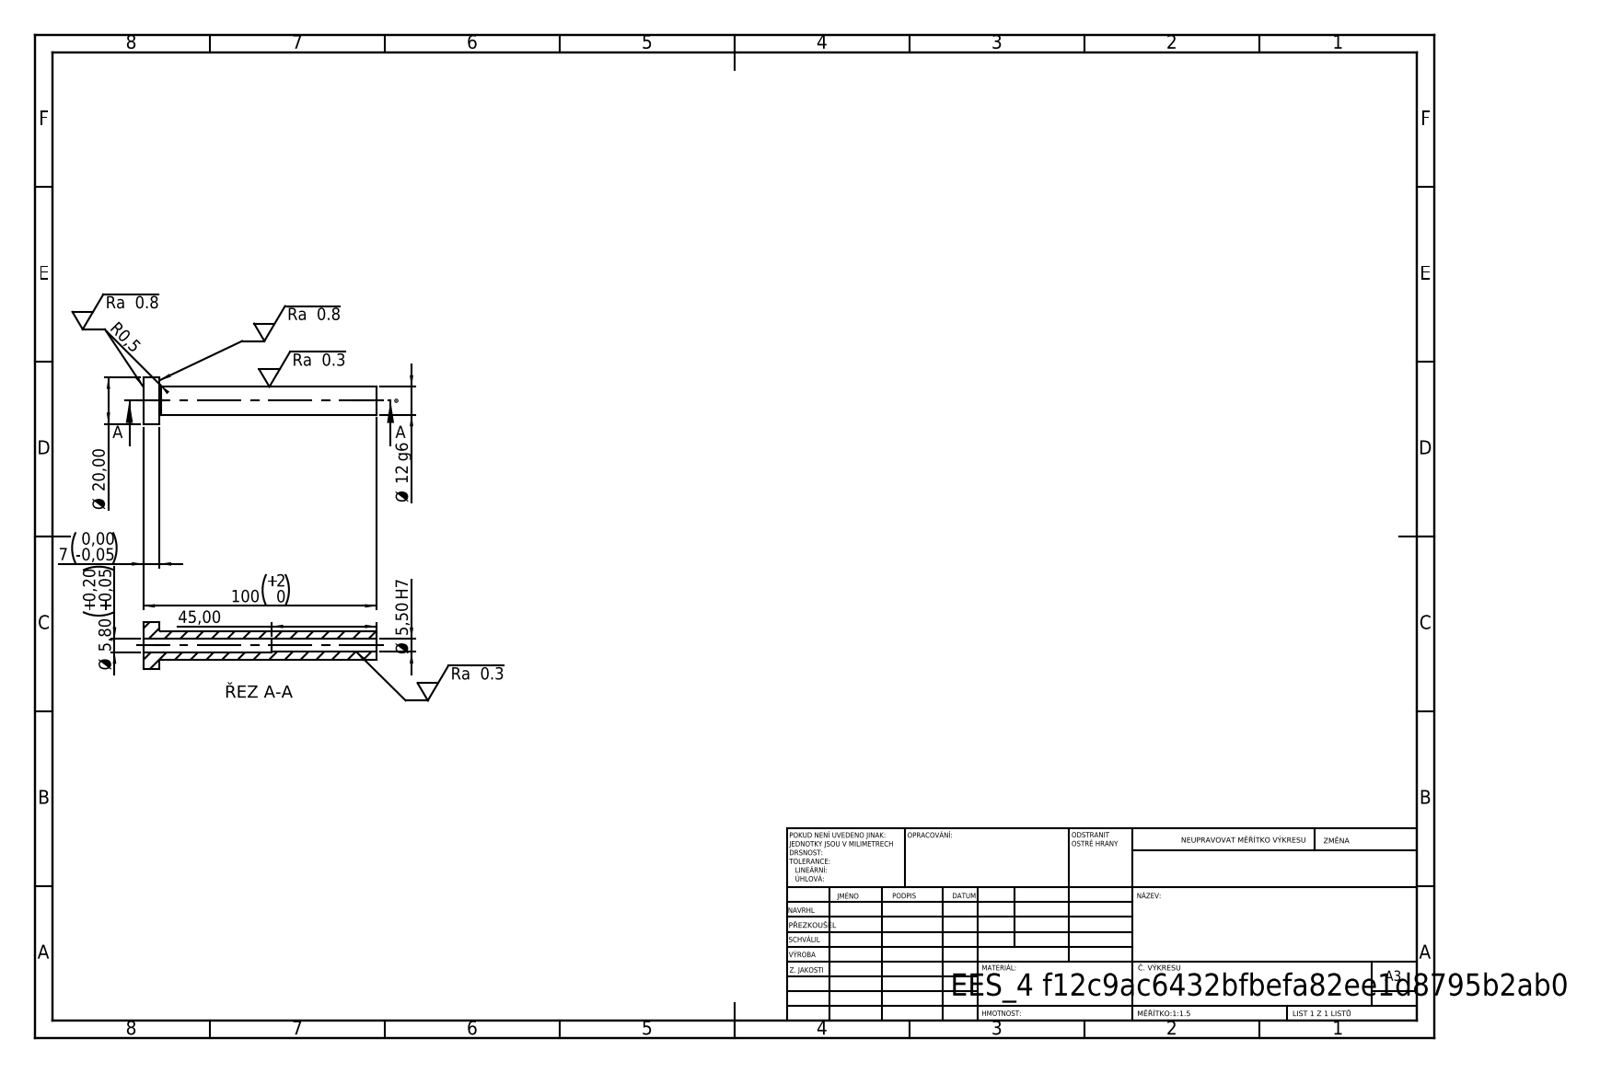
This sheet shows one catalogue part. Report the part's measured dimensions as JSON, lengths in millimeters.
{"step_written_by": "SolidWorks 2019 (CONFIG_CONTROL_DESIGN)", "units": "millimeters", "bodies": {"solids": 1, "faces": 14, "planar": 4, "cylindrical": 8, "other": 2}, "overall_size": [100, 20, 20], "volume_mm3": 10197, "surface_area_mm2": 6298, "round_holes": [[5.5, 1], [5.8, 1]], "round_bosses_or_shafts": [[20, 1], [12, 1]], "face_to_face_distances": [7, 100, 93, 55, 48, 45]}
